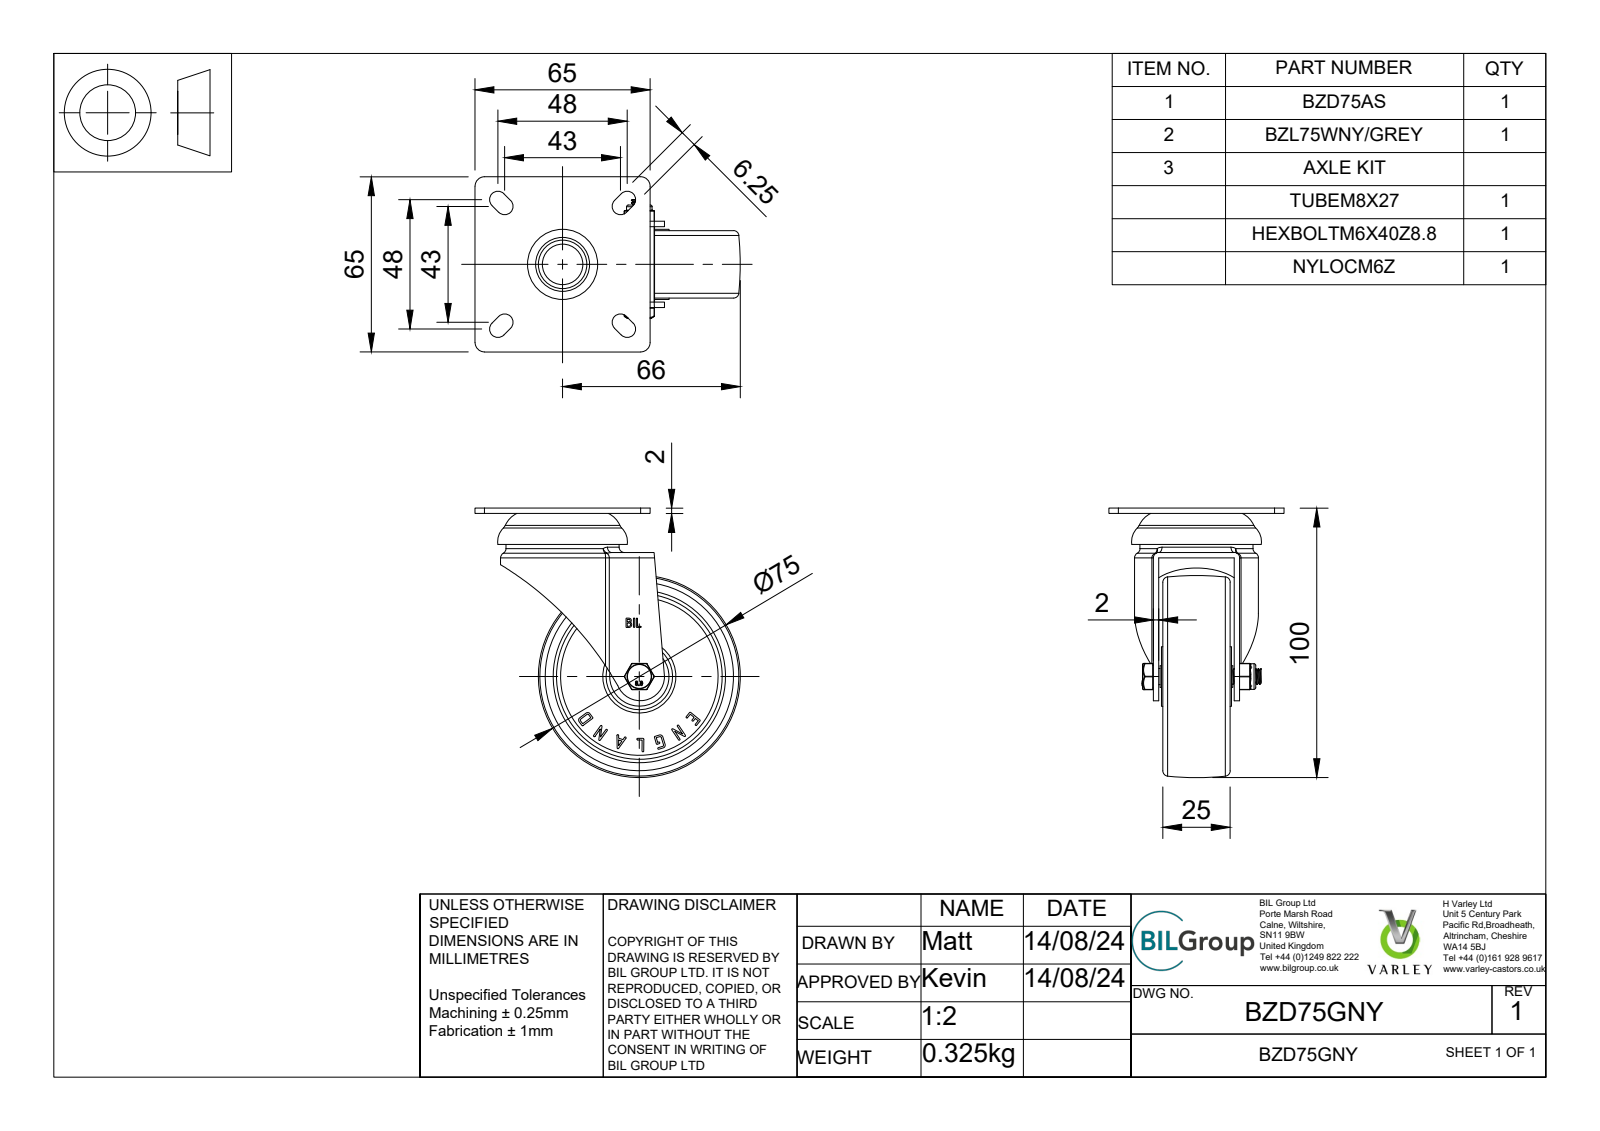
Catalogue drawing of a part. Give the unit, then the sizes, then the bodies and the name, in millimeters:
Units: millimetres
Overall size (bounding box): 100 × 98.5 × 65
Round holes (diameter × count): ⌀6 ×1, ⌀6.2 ×1, ⌀7 ×1, ⌀8.2 ×1, ⌀20 ×1, ⌀38 ×1, ⌀42 ×1, ⌀45.14 ×1, ⌀61.5 ×1
Round bosses / shafts (diameter × count): ⌀37 ×1, ⌀18 ×1, ⌀17 ×1, ⌀10 ×1, ⌀9.5 ×1, ⌀8.5 ×1, ⌀8 ×1, ⌀5.88 ×1
Partial cylindrical surfaces — rounded edges, fillets, slot ends (radius × count): R0.25 ×14, R0.75 ×10, R1.5 ×10, R3.12 ×8, R0.23 ×4, R0.45 ×4, R2 ×4, R3.5 ×4
Main face-to-face distances: 2, 6, 11, 17, 13, 19, 30, 9.5, 3.5, 4
Volume: 89 235 mm³ · Surface area: 50 406 mm²
Bodies: 27 solids, 532 faces (213 planar, 132 cylindrical, 187 other)
Part name (STEP PRODUCT): BZD75GNY v3; BZD75AS v1; ZINC PLATED, PRESSED STEEL TOP PLATE; ZINC PLATED, PRESSED STEEL TOP PLATE Geometry (+7 more)
STEP written by: Autodesk Translation Framework v13.14.0.145 (AUTOMOTIVE_DESIGN)
